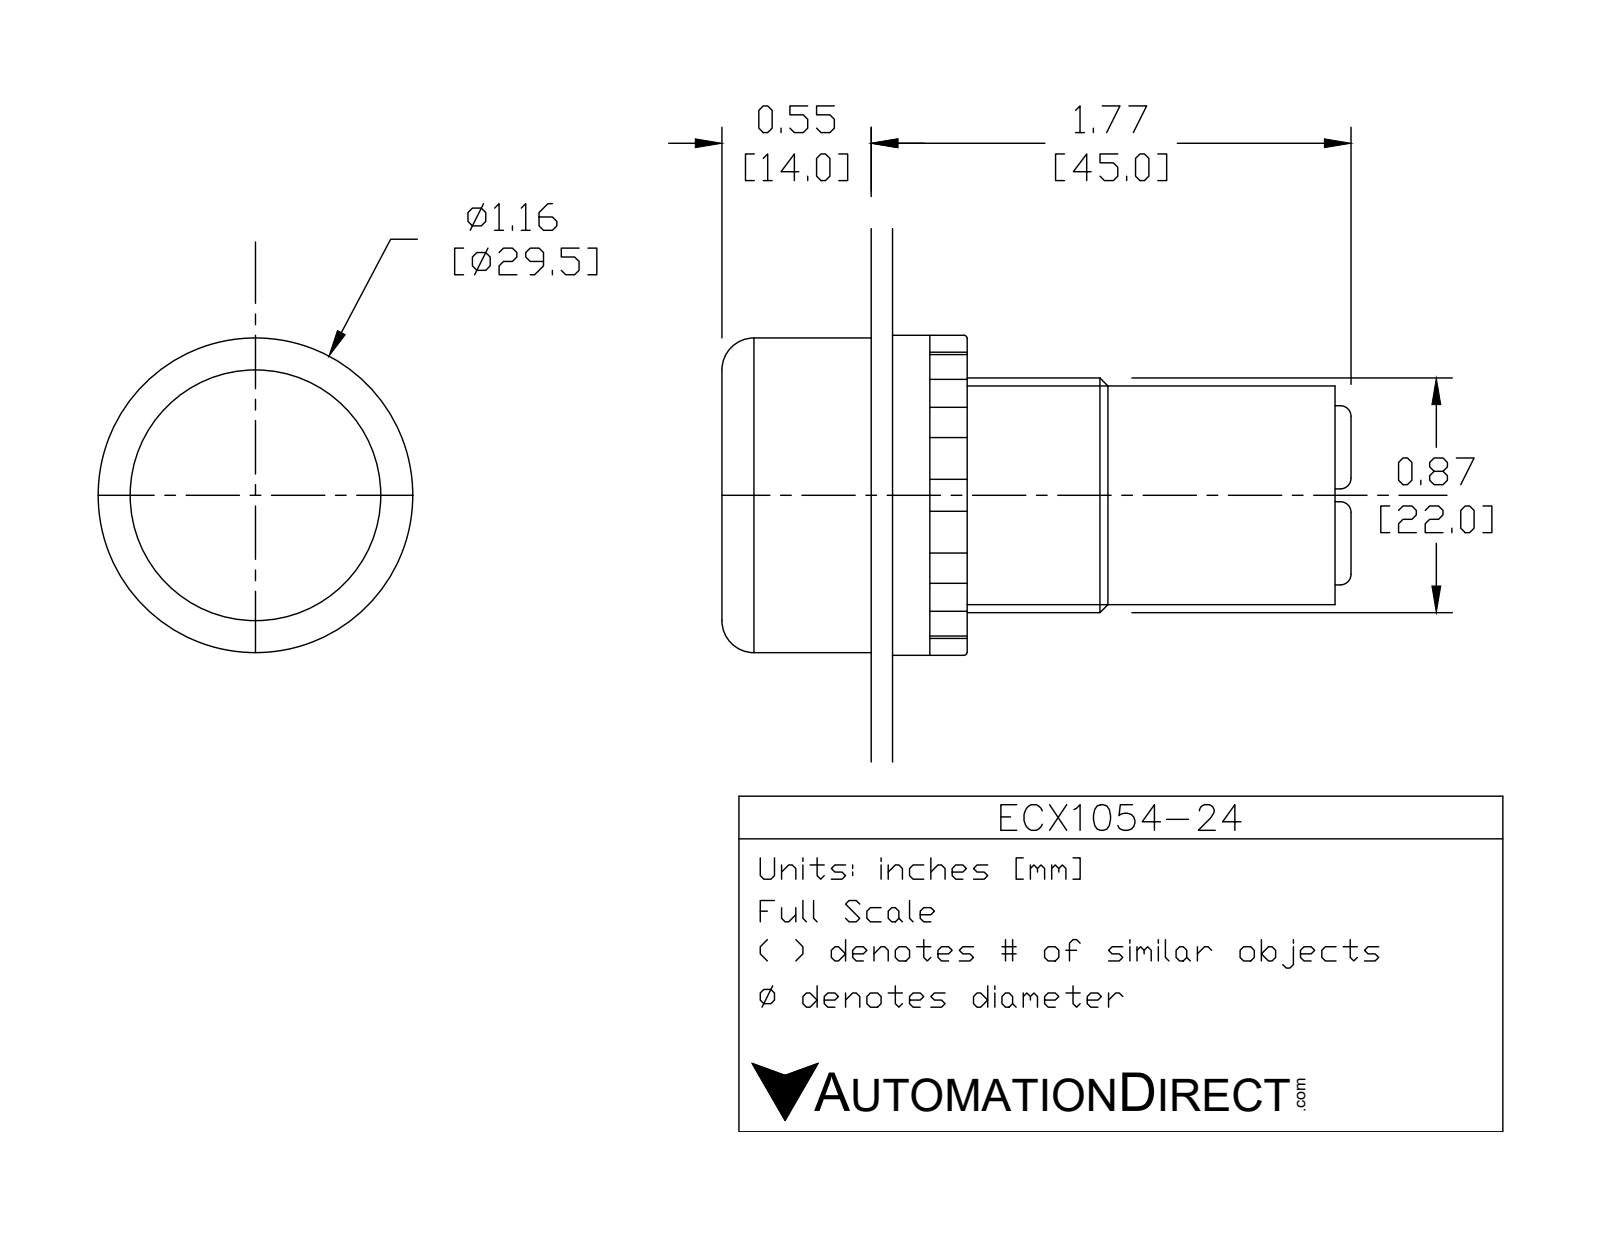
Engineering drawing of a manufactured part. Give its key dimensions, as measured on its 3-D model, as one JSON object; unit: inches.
{"part_name": "ECX1054-24L", "step_written_by": "SolidWorks 2017 (AUTOMOTIVE_DESIGN)", "units": "inches", "bodies": {"solids": 6, "faces": 125, "planar": 63, "cylindrical": 41, "other": 21}, "overall_size": [2.323, 1.181, 1.181], "volume_in3": 1.605, "surface_area_in2": 15.04, "round_holes": [[0.217, 2], [0.886, 1]], "round_bosses_or_shafts": [[0.157, 2], [1.181, 1], [1.142, 1], [1.043, 1], [0.866, 1], [0.787, 1]], "partial_cylinders_radius": [[0.039, 12], [0.354, 1]], "face_to_face_distances": [0.531, 0.02, 0.551, 0.787, 0.236, 0.256, 1.535, 0.276, 0.512, 1.063], "hole_center_spacings": [0.182, 0.364]}
